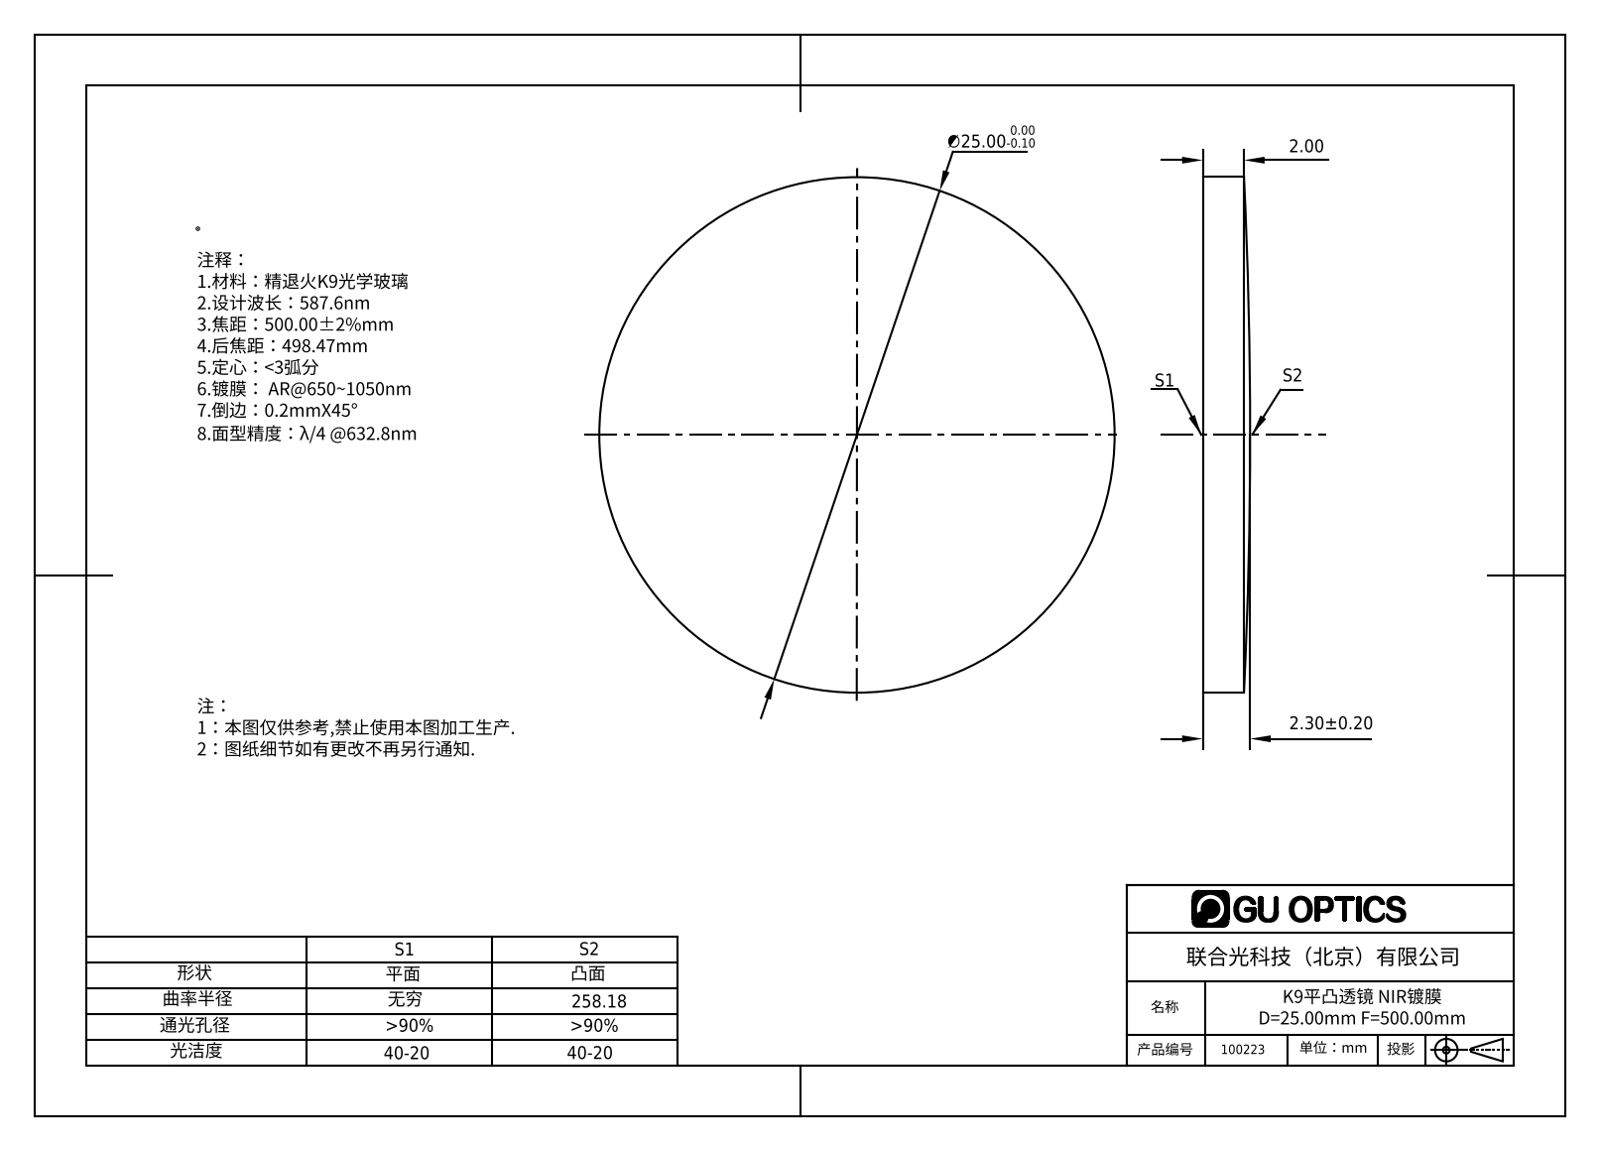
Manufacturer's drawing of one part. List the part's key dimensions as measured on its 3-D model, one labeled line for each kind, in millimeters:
Part name (STEP PRODUCT): 100223
STEP written by: SolidWorks 2016 (AUTOMOTIVE_DESIGN)
Units: millimetres
Bodies: 1 solid, 5 faces (1 planar, 2 cylindrical, 2 other)
Overall size (bounding box): 25 × 25 × 2.3
Volume: 1 055 mm³ · Surface area: 1 139 mm²
Round bosses / shafts (diameter × count): ⌀25 ×1
